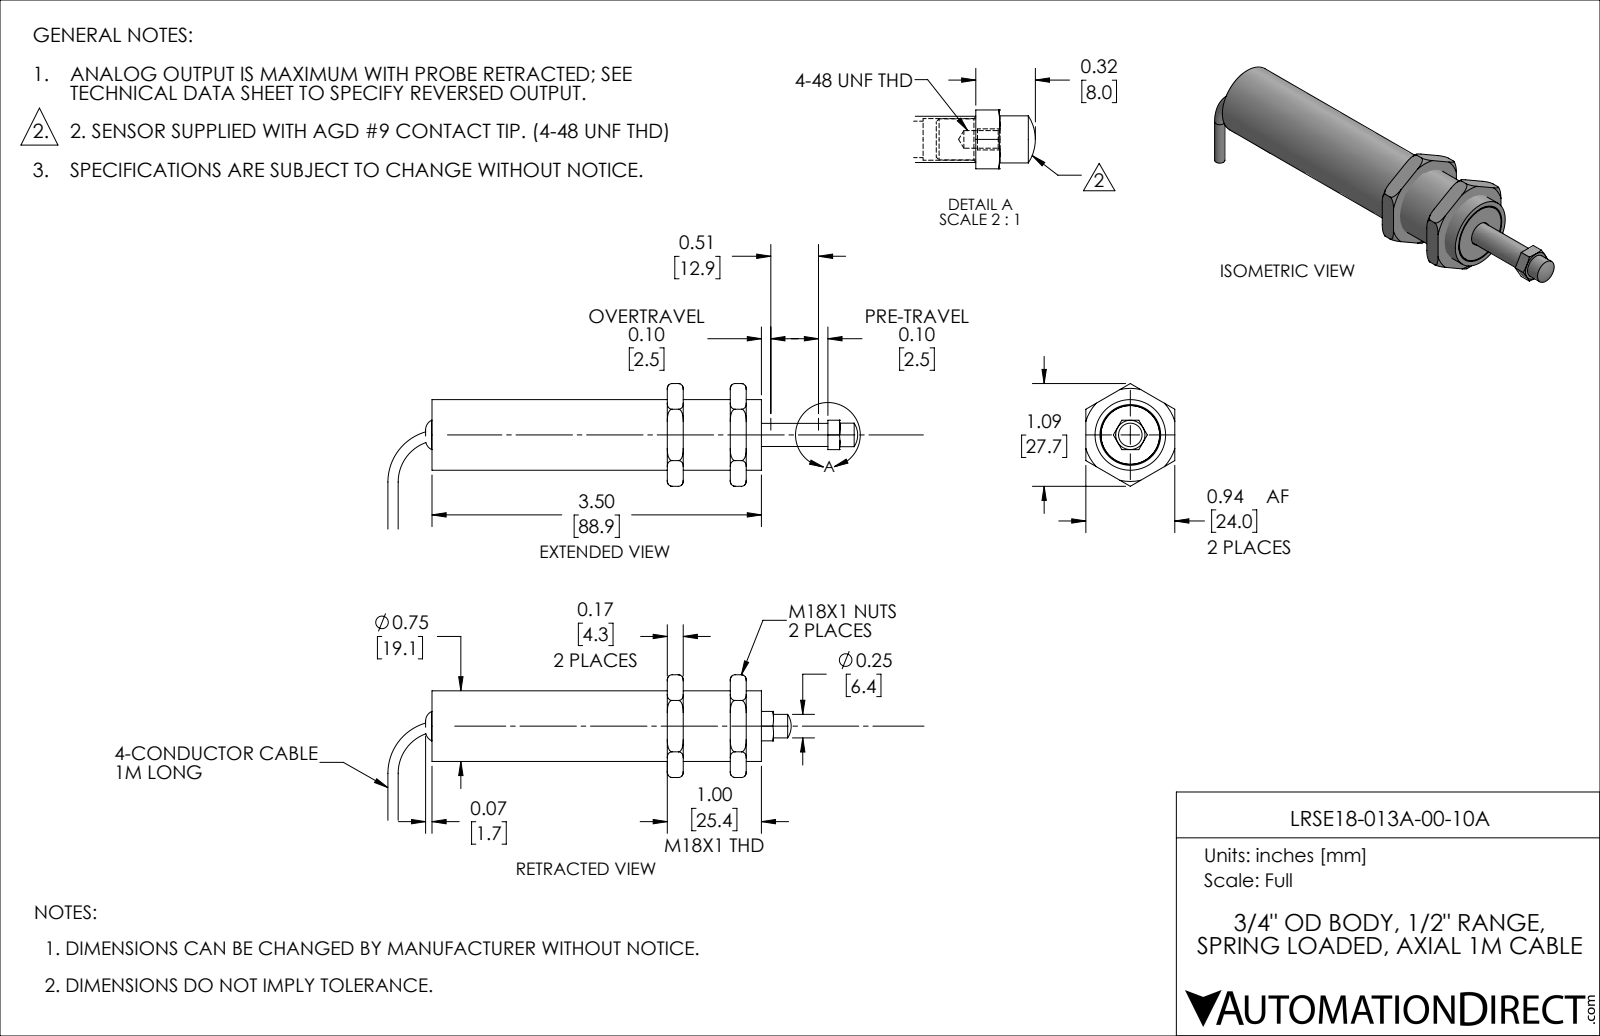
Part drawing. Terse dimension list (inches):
name: LRSE18-013A-00-10A
written by: SolidWorks 2019 (AUTOMOTIVE_DESIGN)
unit: in
bodies: 11 solids, 115 faces (48 planar, 26 cylindrical, 41 other)
size: 4.285 × 1.546 × 0.945
volume: 0.904 in³; area: 27.36 in²
holes: 1× ⌀0.093, 1× ⌀0.109, 1× ⌀0.188, 1× ⌀0.261, 1× ⌀0.307, 1× ⌀0.5, 1× ⌀0.62, 1× ⌀0.625, 1× ⌀0.65, 1× ⌀0.665, 1× ⌀0.71, 1× ⌀0.725
bosses: 1× ⌀0.75, 1× ⌀0.7, 1× ⌀0.685, 1× ⌀0.624, 1× ⌀0.25, 1× ⌀0.218, 1× ⌀0.112, 1× ⌀0.109
face distances: 0.669, 0.169, 0.945, 2.864, 1.864, 2.533, 1, 0.331, 2.033, 2.703
